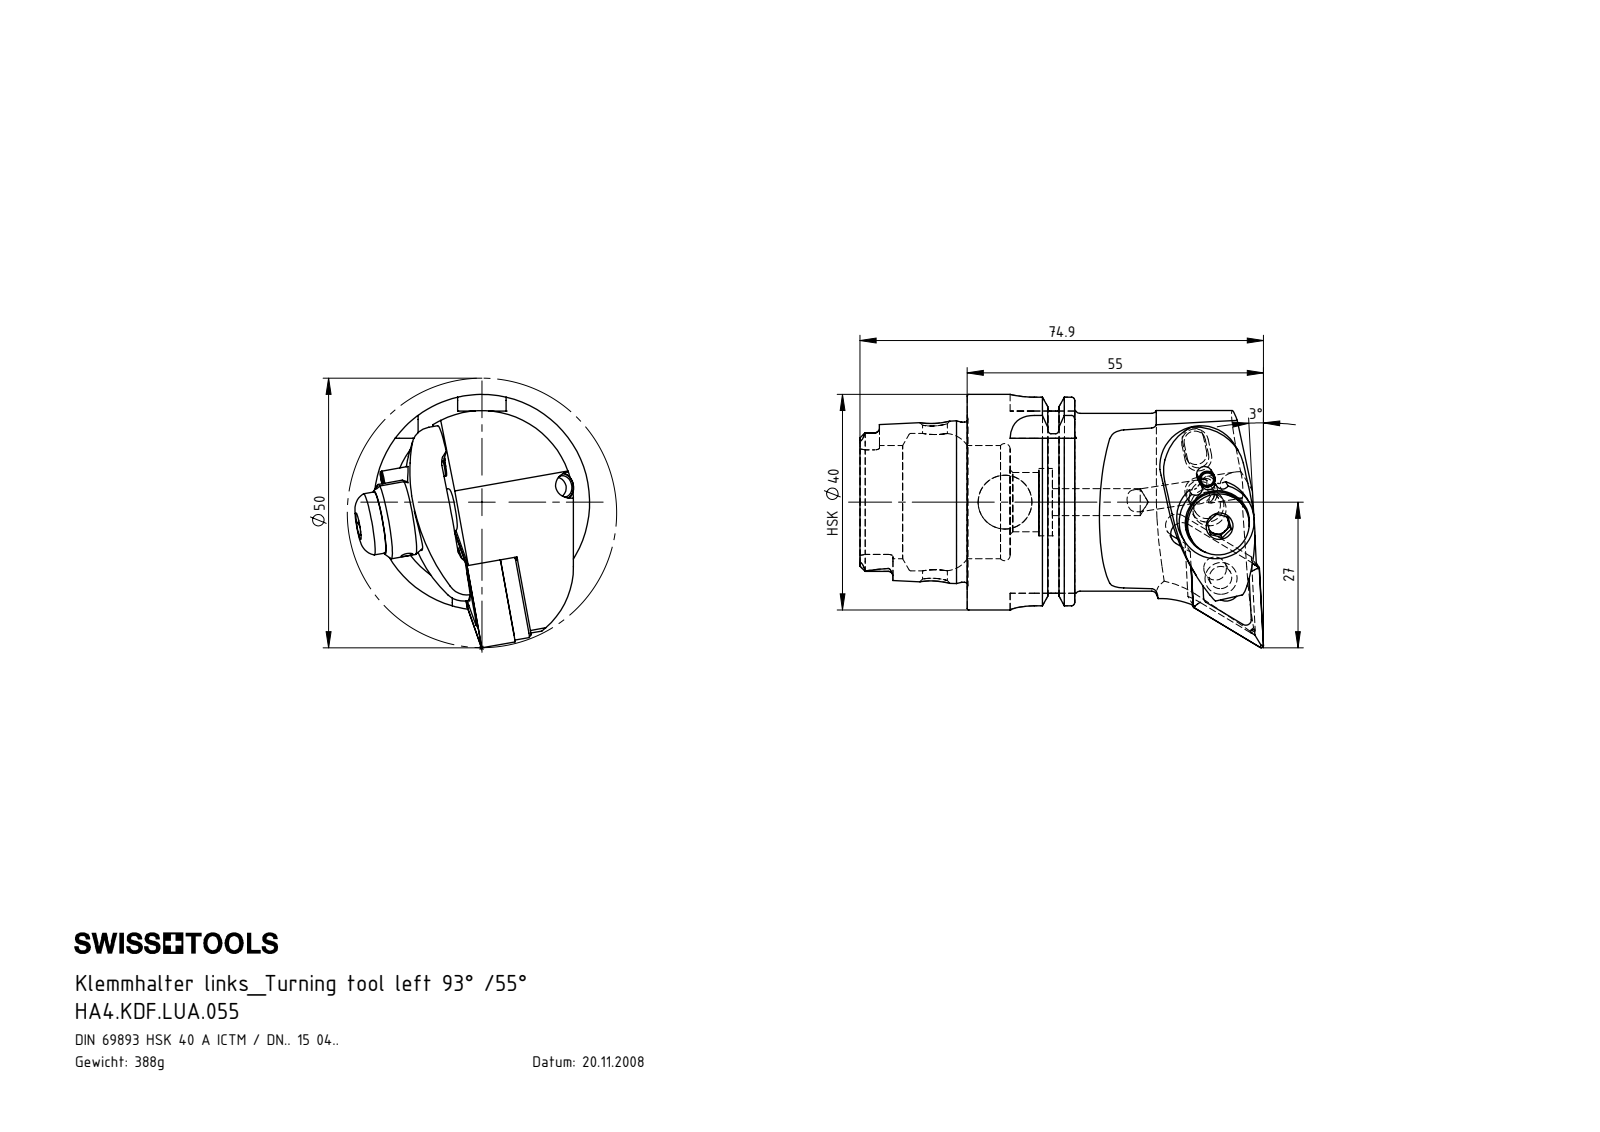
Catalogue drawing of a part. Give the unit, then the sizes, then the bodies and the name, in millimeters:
Units: millimetres
Overall size (bounding box): 74.9 × 47 × 43.57
Round holes (diameter × count): ⌀2 ×3, ⌀5 ×3, ⌀4.2 ×2, ⌀7 ×2, ⌀2.4 ×1, ⌀3 ×1, ⌀4 ×1, ⌀4.6 ×1, ⌀5.16 ×1, ⌀6.2 ×1, ⌀6.5 ×1, ⌀8.5 ×1
Round bosses / shafts (diameter × count): ⌀5 ×2, ⌀3 ×2, ⌀40 ×1, ⌀34.75 ×1, ⌀33 ×1, ⌀29.71 ×1, ⌀14 ×1, ⌀11.5 ×1
Partial cylindrical surfaces — rounded edges, fillets, slot ends (radius × count): R0.39 ×6, R0.69 ×6, R0.9 ×6, R0.4 ×5, R4.5 ×4, R1.5 ×3, R3 ×3, R1.82 ×2
Main face-to-face distances: 6.02, 9.2, 3.18, 7.95, 12, 10.52, 7.34, 1.32, 12.69, 19.95
Hole centre spacings: 15.01, 7.99, 23, 8.19, 14.81, 15, 23.01, 8
Volume: 50 378 mm³ · Surface area: 19 424 mm²
Bodies: 11 solids, 468 faces (125 planar, 154 cylindrical, 189 other)
Part name (STEP PRODUCT): WCC-ER2.001.010_A; WCC-ER5.102.005_A; HA4.KDF.LUA.055; HA4-KDF.LUA.055_C_Fertigbearbeitung (+7 more)
STEP written by: SolidWorks 2017 (AUTOMOTIVE_DESIGN)
